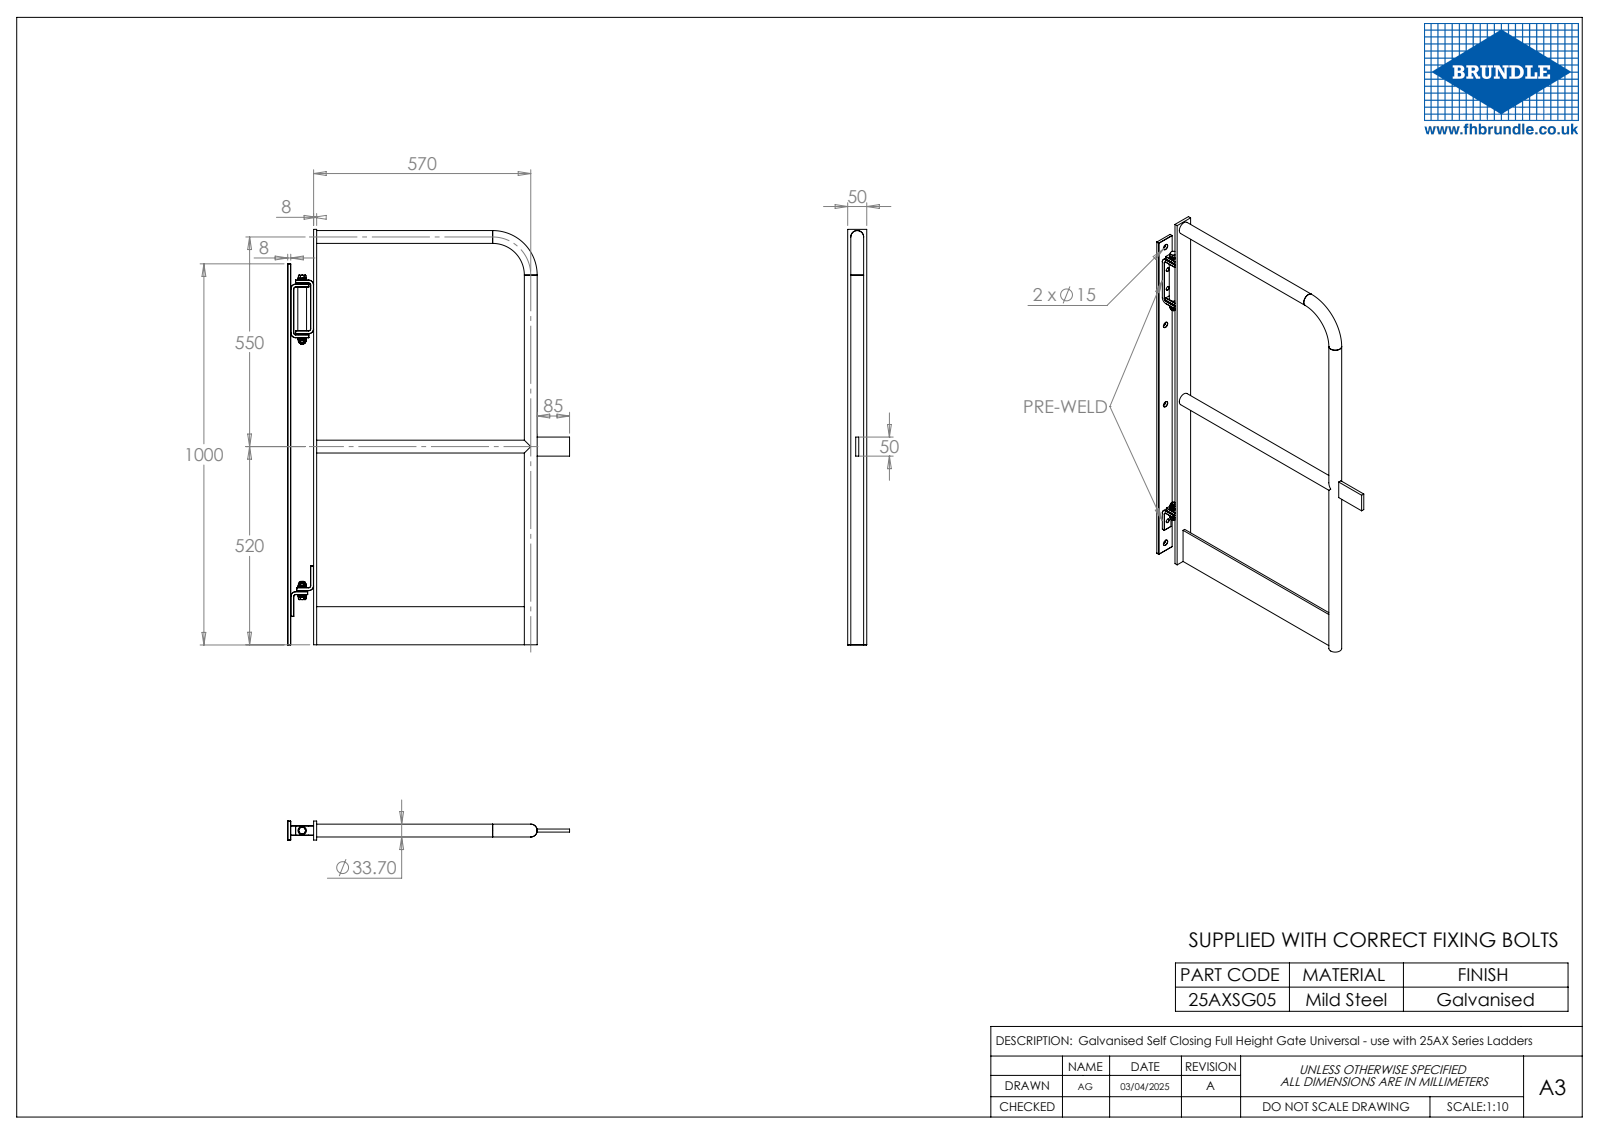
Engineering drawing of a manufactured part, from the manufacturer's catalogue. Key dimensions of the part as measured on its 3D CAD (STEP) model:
Part name (STEP PRODUCT): Bolt & Nuts^25AXSG05 Assem1; Spring^25AXSG05 Assem1; Hinge U-Shape Plates^25AXSG05 Assem1; Kick Plate 100 x 6^25AXSG05 (+8 more)
STEP written by: SolidWorks 2023 (CONFIG_CONTROL_DESIGN)
Units: millimetres
Bodies: 30 solids, 502 faces (253 planar, 119 cylindrical, 130 other)
Overall size (bounding box): 1090.5 × 739.85 × 50
Volume: 1 919 000 mm³ · Surface area: 864 635 mm²
Round holes (diameter × count): ⌀10 ×5, ⌀15 ×4, ⌀28.5 ×3, ⌀9 ×1
Round bosses / shafts (diameter × count): ⌀33.7 ×3, ⌀23 ×1, ⌀22 ×1, ⌀20 ×1, ⌀15 ×1, ⌀8 ×1
Partial cylindrical surfaces — rounded edges, fillets, slot ends (radius × count): R5 ×6, R13 ×6
Main face-to-face distances: 8, 68, 60, 6, 76, 22, 28, 50, 12.5, 21
Hole centre spacings: 10.5, 60, 49.5, 50.5, 58, 68.5, 70.5, 74.5
